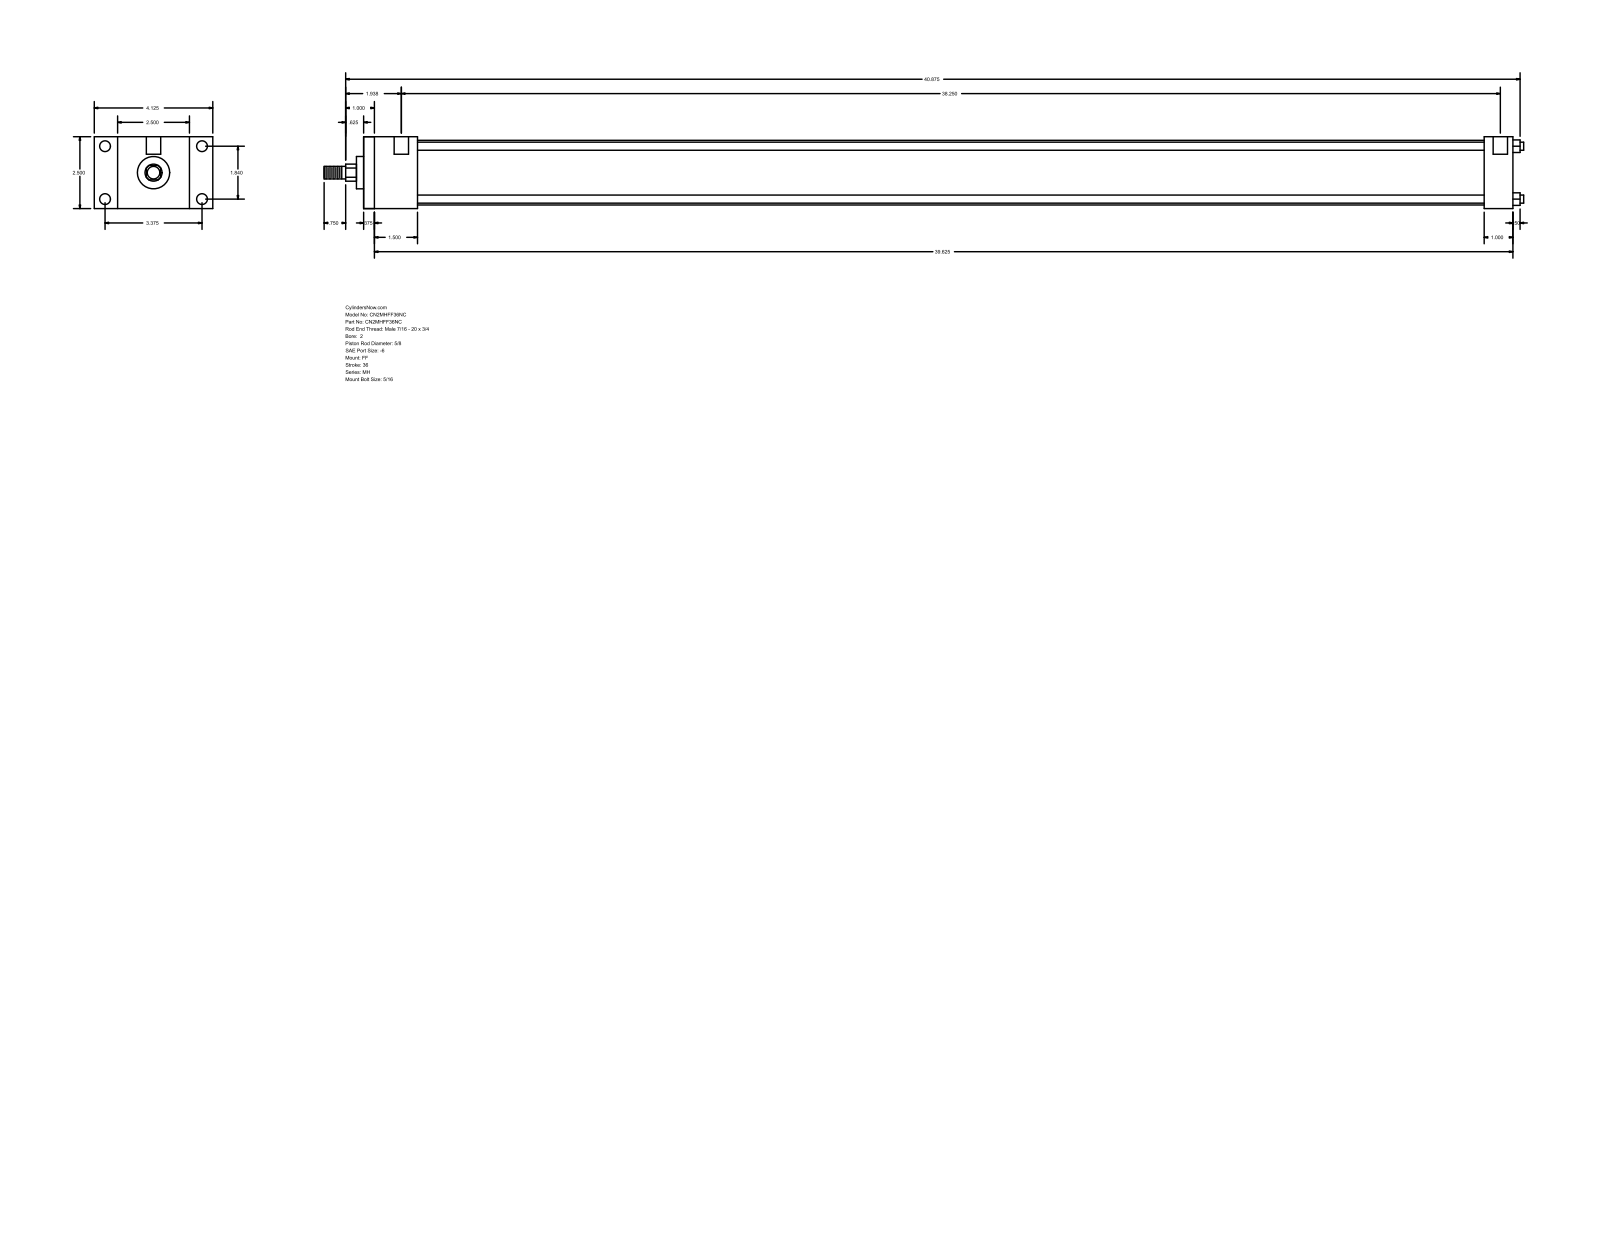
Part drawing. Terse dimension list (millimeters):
name: MH_FF__0200_0.625
written by: GSSL Pune (CONFIG_CONTROL_DESIGN)
unit: mm
bodies: 0 solids, 92 faces (64 planar, 28 cylindrical, 0 other)
size: 1060.45 × 104.78 × 63.5
holes: 4× ⌀5.56, 4× ⌀9.53, 2× ⌀12.7
bosses: 4× ⌀7.14, 1× ⌀57.15, 1× ⌀28.57, 1× ⌀15.88, 1× ⌀11.11
rounds: 1× R7.54
face distances: 63.5, 1016, 9.52, 1006.48, 25.4, 38.1, 47.62, 990.6, 981.08, 942.98
hole spacings: 46.74, 85.72, 97.63, 979.49, 3.18, 4.76, 971.55, 974.73
